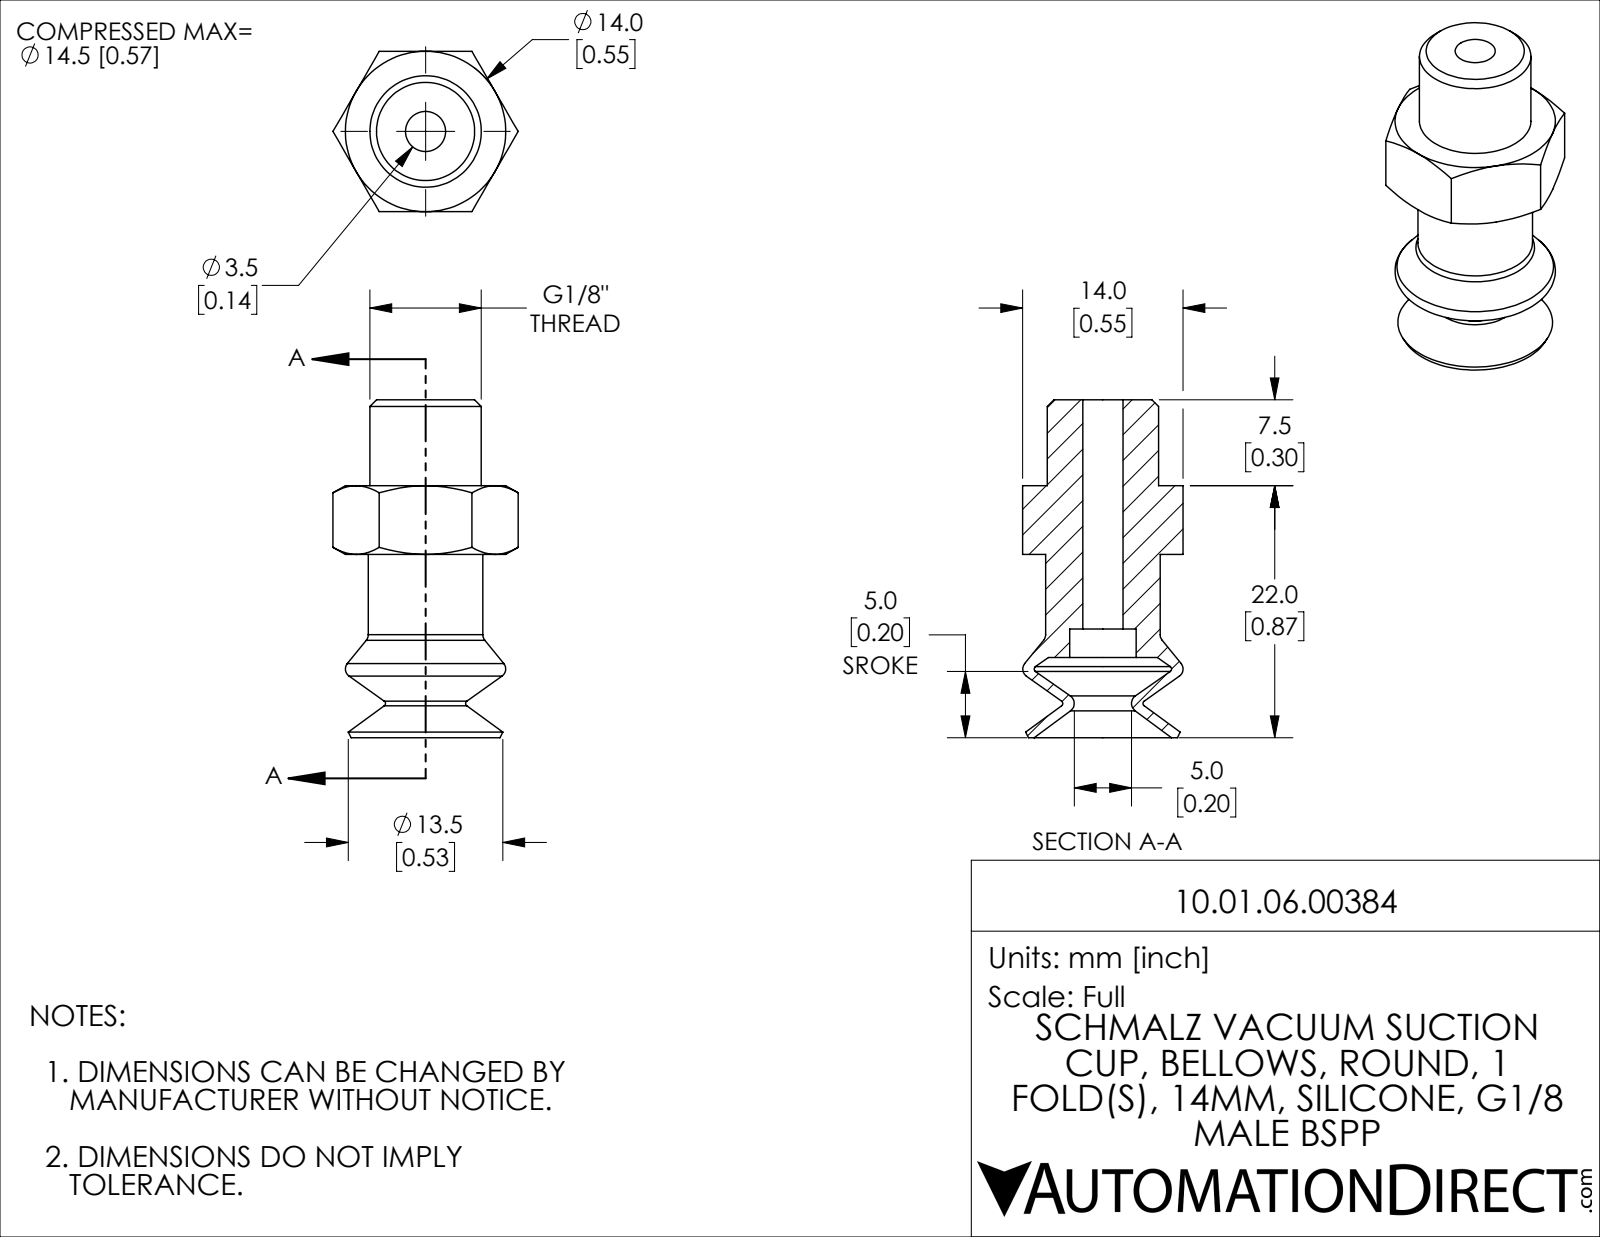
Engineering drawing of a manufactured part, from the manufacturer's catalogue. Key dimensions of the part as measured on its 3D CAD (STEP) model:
Part name (STEP PRODUCT): 10.01.06.00384
STEP written by: SolidWorks 2021 (CONFIG_CONTROL_DESIGN)
Units: millimetres
Bodies: 1 solid, 64 faces (12 planar, 8 cylindrical, 44 other)
Overall size (bounding box): 29.5 × 16.17 × 14
Volume: 2 334 mm³ · Surface area: 2 064 mm²
Round holes (diameter × count): ⌀3.5 ×1, ⌀5.8 ×1
Round bosses / shafts (diameter × count): ⌀10 ×1, ⌀9.73 ×1
Main face-to-face distances: 14, 6, 13.5, 7.5, 9, 15, 22.5, 7, 16, 22
